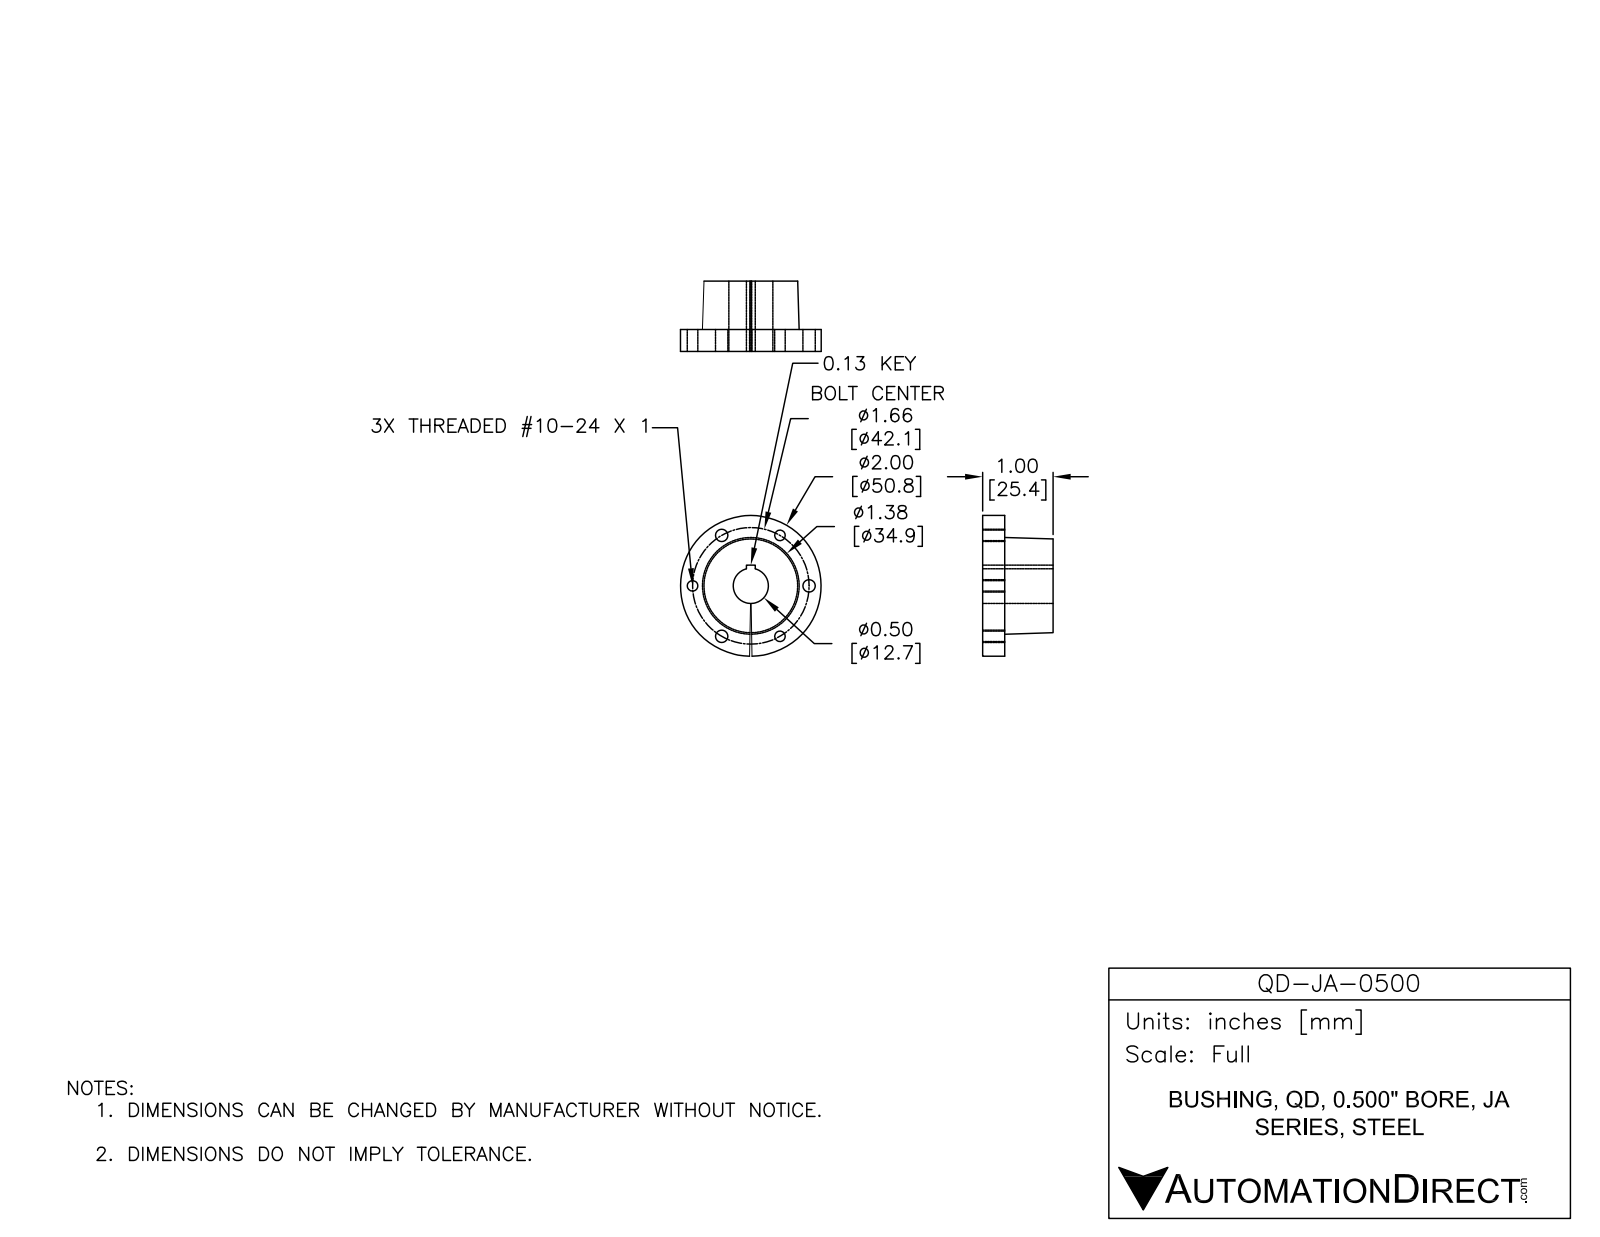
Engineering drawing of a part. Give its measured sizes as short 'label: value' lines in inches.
name: QD-JA-0500
written by: SolidWorks 2014 (AUTOMOTIVE_DESIGN)
unit: in
bodies: 1 solid, 29 faces (8 planar, 18 cylindrical, 3 other)
size: 2 × 2 × 1
volume: 1.718 in³; area: 14.07 in²
holes: 3× ⌀0.149, 3× ⌀0.175, 1× ⌀0.5
bosses: 1× ⌀2
face distances: 0.313, 1, 0.687, 0.125
hole spacings: 0.828, 0.828, 1.434, 1.435, 1.657, 1.656
